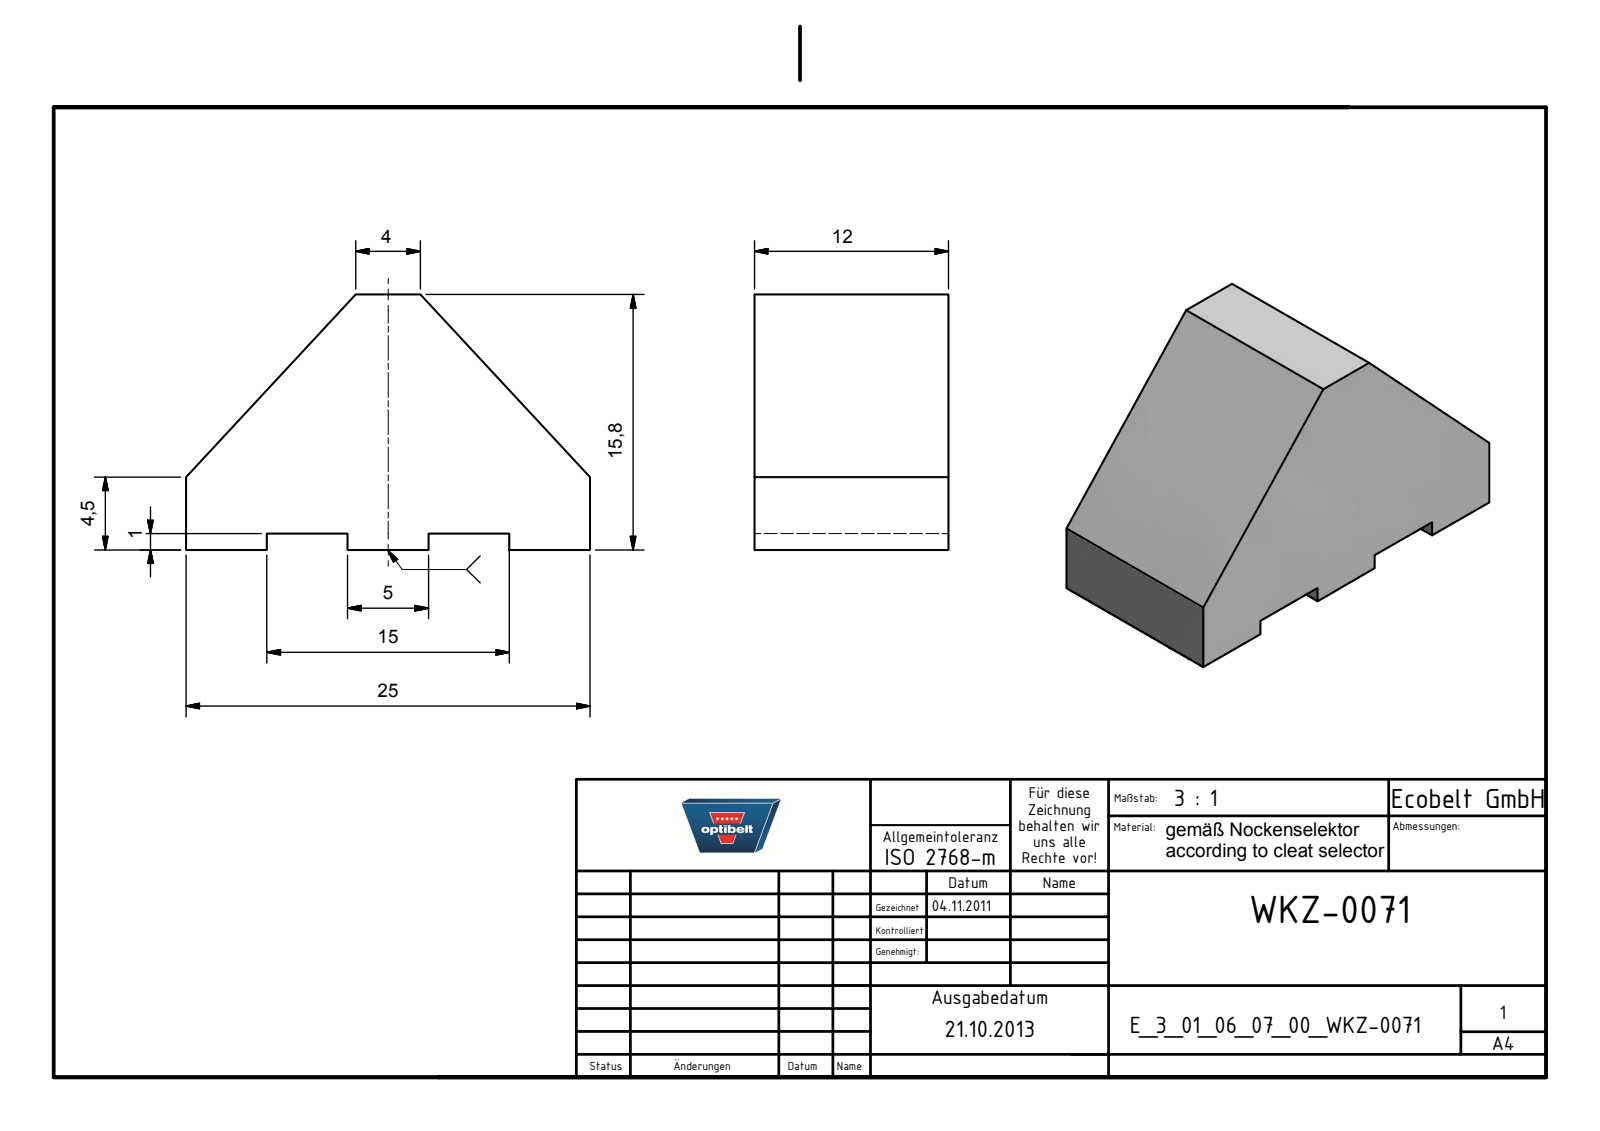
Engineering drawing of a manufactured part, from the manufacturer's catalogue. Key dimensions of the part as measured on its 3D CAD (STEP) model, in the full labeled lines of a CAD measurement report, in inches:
Part name (STEP PRODUCT): E_3_01_06_07_00_WKZ-0071
STEP written by: Autodesk Inventor 2025 (AUTOMOTIVE_DESIGN)
Units: inches
Bodies: 1 solid, 16 faces (16 planar, 0 cylindrical, 0 other)
Overall size (bounding box): 0.984 × 0.622 × 0.472
Volume: 0.195 in³ · Surface area: 2.181 in²
Main face-to-face distances: 0.472, 0.039, 0.197, 0.984, 0.622, 0.583, 0.394, 0.591, 0.787
